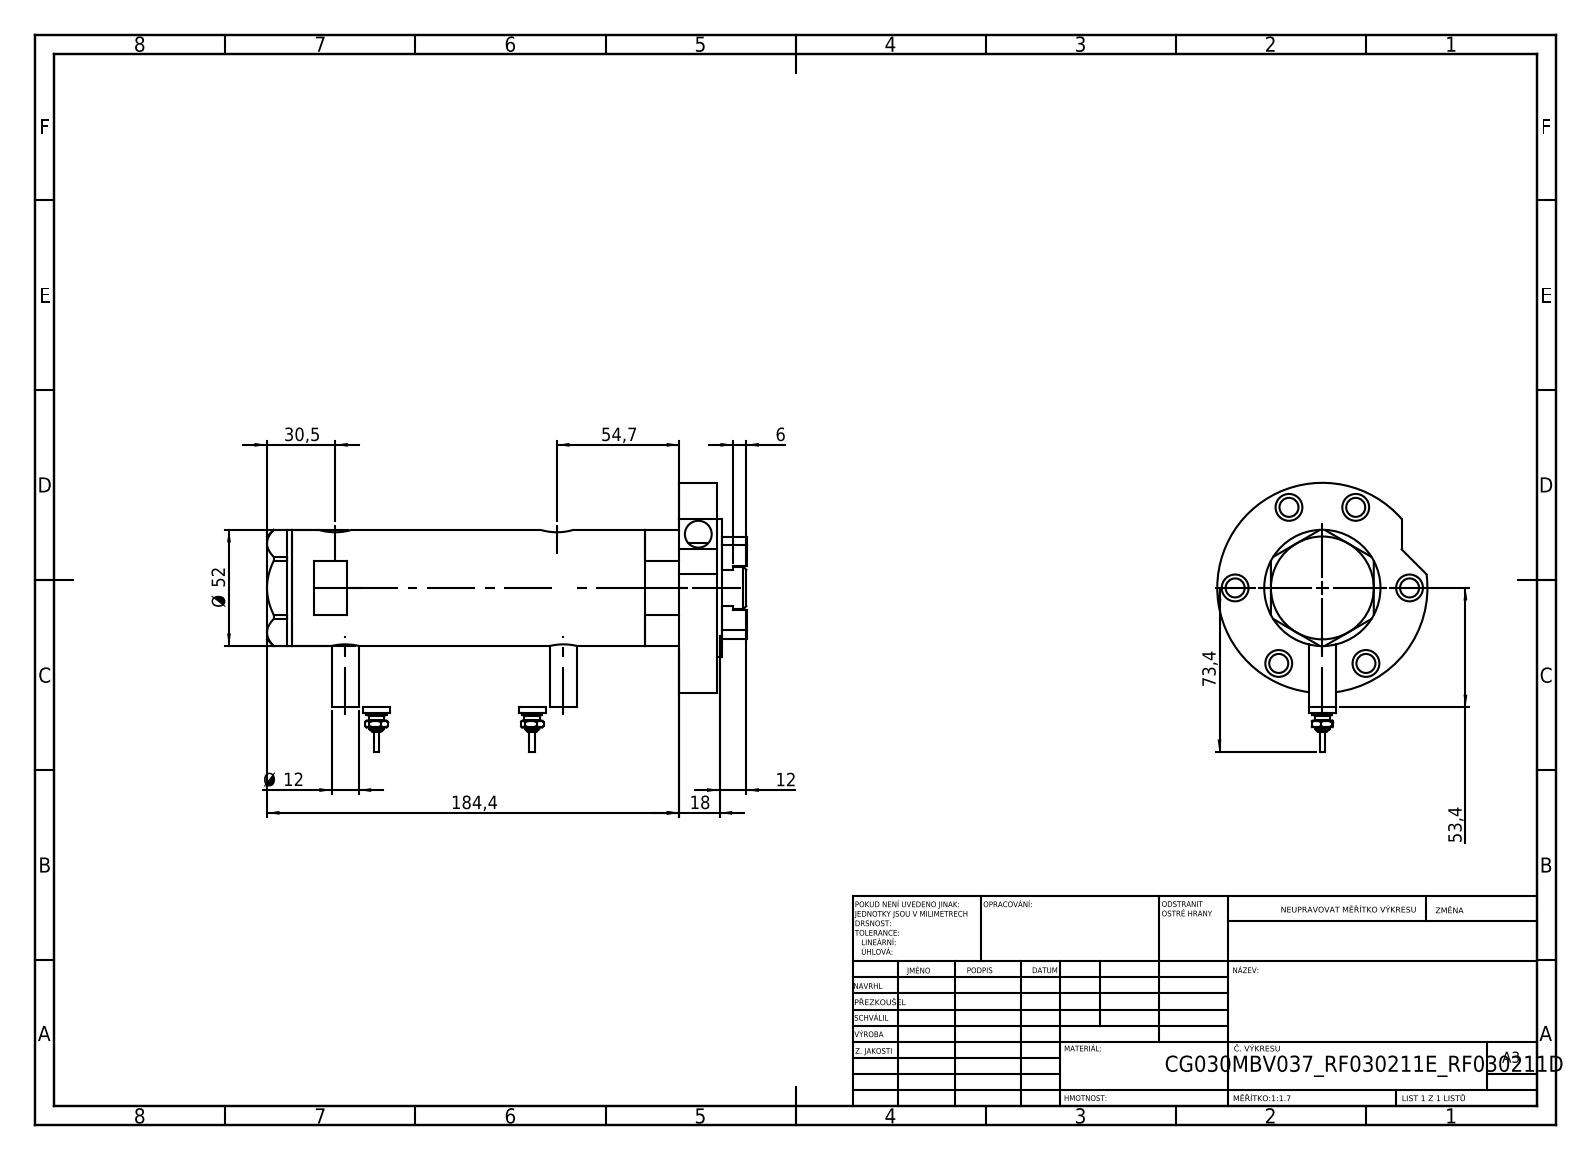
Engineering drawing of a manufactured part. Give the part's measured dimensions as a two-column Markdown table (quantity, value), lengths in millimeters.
| quantity | value |
| --- | --- |
| part name | V270CG_FRONT; V270CG_RF211E; V270CG_VC; Switch (+3 more) |
| STEP written by | SolidWorks 2019 (CONFIG_CONTROL_DESIGN) |
| units | millimeters |
| bodies | 9 solids, 310 faces (128 planar, 118 cylindrical, 64 other) |
| overall size | 214.6 × 120.4 × 94 |
| volume | 487 986 mm³ |
| surface area | 117 449 mm² |
| round holes (diameter × count) | 12 × 7, 8.5 × 6, 5.1 × 4, 9 × 4, 9.73 × 2, 12.5 × 2, 15 × 2, 6.5 × 1, 20 × 1, 21.5 × 1, 30 × 1, 33 × 1 |
| round bosses / shafts (diameter × count) | 12 × 4, 9 × 2, 7 × 2, 4.5 × 2, 2.5 × 2, 94 × 1, 62 × 1, 52 × 1 |
| main face-to-face distances | 17, 173.4, 190.4, 2, 11, 192.4, 121.5, 51.9, 68.9, 203.4 |
| hole center spacings | 39, 16.74, 37.57, 46.81, 10, 22.37, 22.95, 28.26 |
